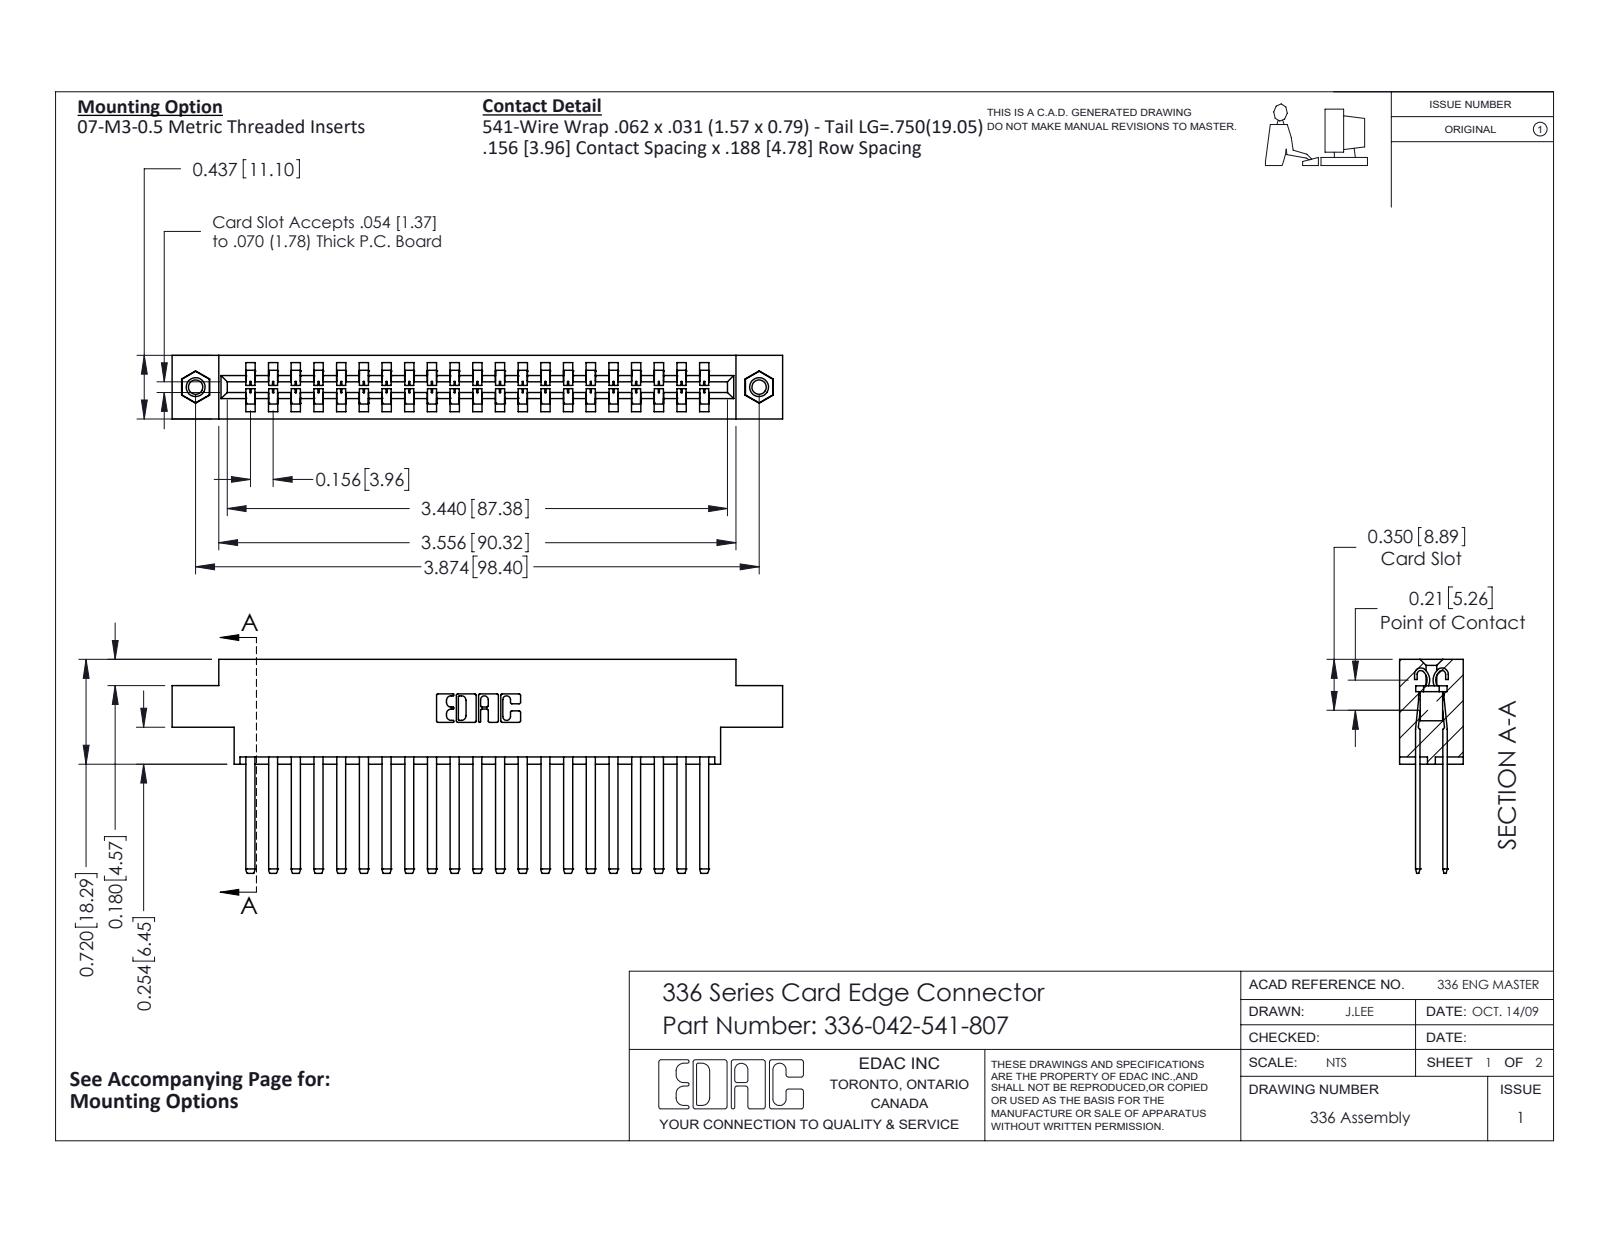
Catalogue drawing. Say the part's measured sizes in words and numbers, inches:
The part is named "336-290-001_336-290-541; 336 Part_Offset - .156 Dia - TI; 336-042-541-807; 345-250-001_345-250-005-103". Its 3-D file was written by "SolidWorks 2020 (CONFIG_CONTROL_DESIGN)". It is 45 solids with 1942 faces: 1198 planar, 728 cylindrical and 16 other. Overall it measures 4.197 by 1.47 by 0.437 inches. Its volume is 0.962 cubic inches and its surface area 30.76 square inches. Round holes: 2 of diameter 0.098, 2 of diameter 0.125, 2 of diameter 0.156. Round bosses or shafts: 2 of diameter 0.155. Partial cylindrical surfaces (rounded edges, fillets, slot ends): 84 of radius 0.004, 42 of radius 0.056, 22 of radius 0.01, 6 of radius 0.007, 6 of radius 0.031, 4 of radius 0.022, 4 of radius 0.04, 3 of radius 0.026. The main face-to-face distances are 0.188, 0.328, 0.14, 0.297, 0.109, 0.031, 0.437, 0.033, 0.181, 0.146. The hole center spacings are 3.874.
